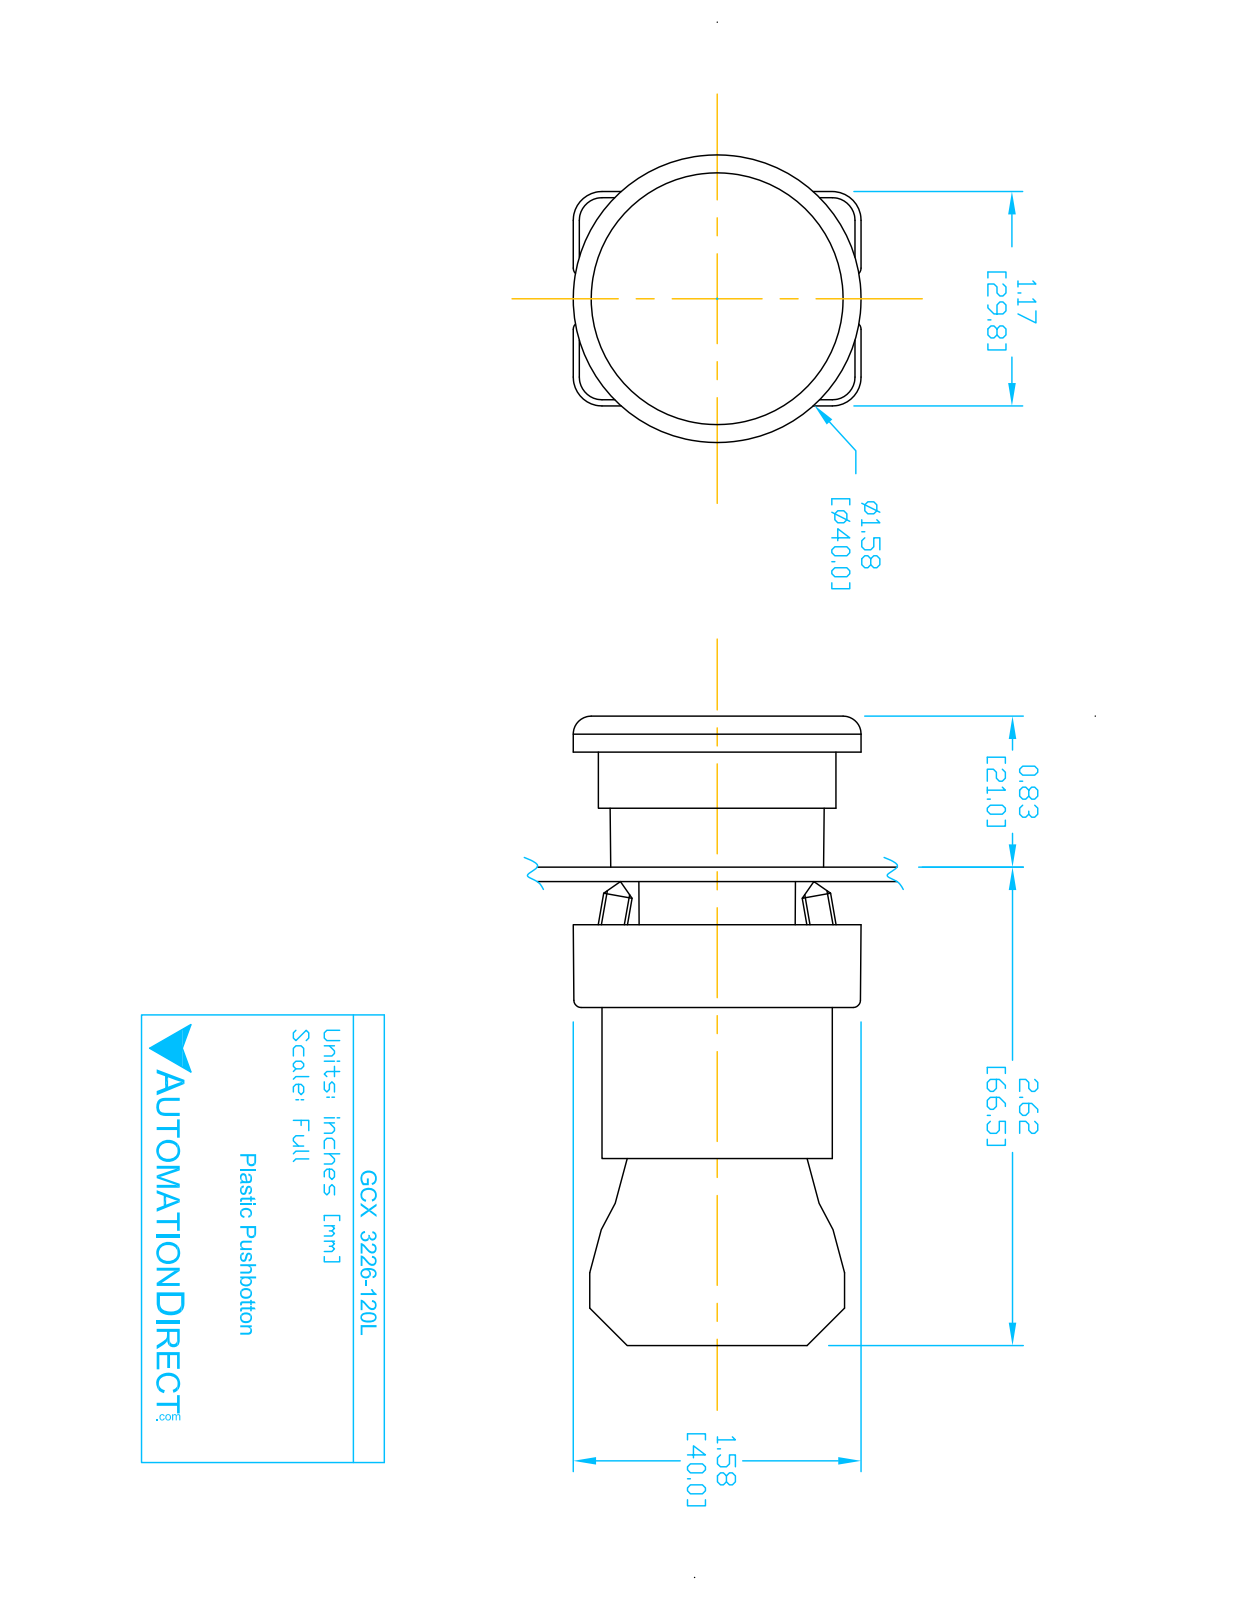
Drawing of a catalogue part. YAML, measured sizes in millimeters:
part_name: "ECX3029-2; ECX1050; GCX322X OPERATOR; GCX3226-120L (+1 more)"
step_written_by: "SolidWorks 2016 (AUTOMOTIVE_DESIGN)"
units: millimeters
bodies: {solids: 7, faces: 431, planar: 252, cylindrical: 146, other: 33}
overall_size: [88.1, 40.2, 40]
volume: 47440
surface_area: 26380
round_holes:
  - {diameter: 2, count: 2}
  - {diameter: 3.1, count: 2}
  - {diameter: 3.3, count: 2}
  - {diameter: 2.2, count: 1}
  - {diameter: 5, count: 1}
  - {diameter: 11.9, count: 1}
  - {diameter: 22.3, count: 1}
  - {diameter: 22.6, count: 1}
  - {diameter: 26, count: 1}
  - {diameter: 30, count: 1}
round_bosses_or_shafts:
  - {diameter: 4, count: 4}
  - {diameter: 33, count: 1}
  - {diameter: 29.8, count: 1}
  - {diameter: 24, count: 1}
  - {diameter: 21.7, count: 1}
  - {diameter: 19.8, count: 1}
  - {diameter: 12.8, count: 1}
partial_cylinders:
  - {radius: 1.5, count: 24}
  - {radius: 1, count: 12}
  - {radius: 3.1, count: 12}
  - {radius: 4, count: 12}
  - {radius: 1, count: 8}
  - {radius: 3.3, count: 2}
  - {radius: 0.5, count: 1}
  - {radius: 1.6, count: 1}
face_to_face_distances: [21, 62.1, 41.1, 14.7, 58.1, 37.1, 4, 14.9, 0.8, 29.6]
hole_center_spacings: [6, 13.7, 12, 12.3]
